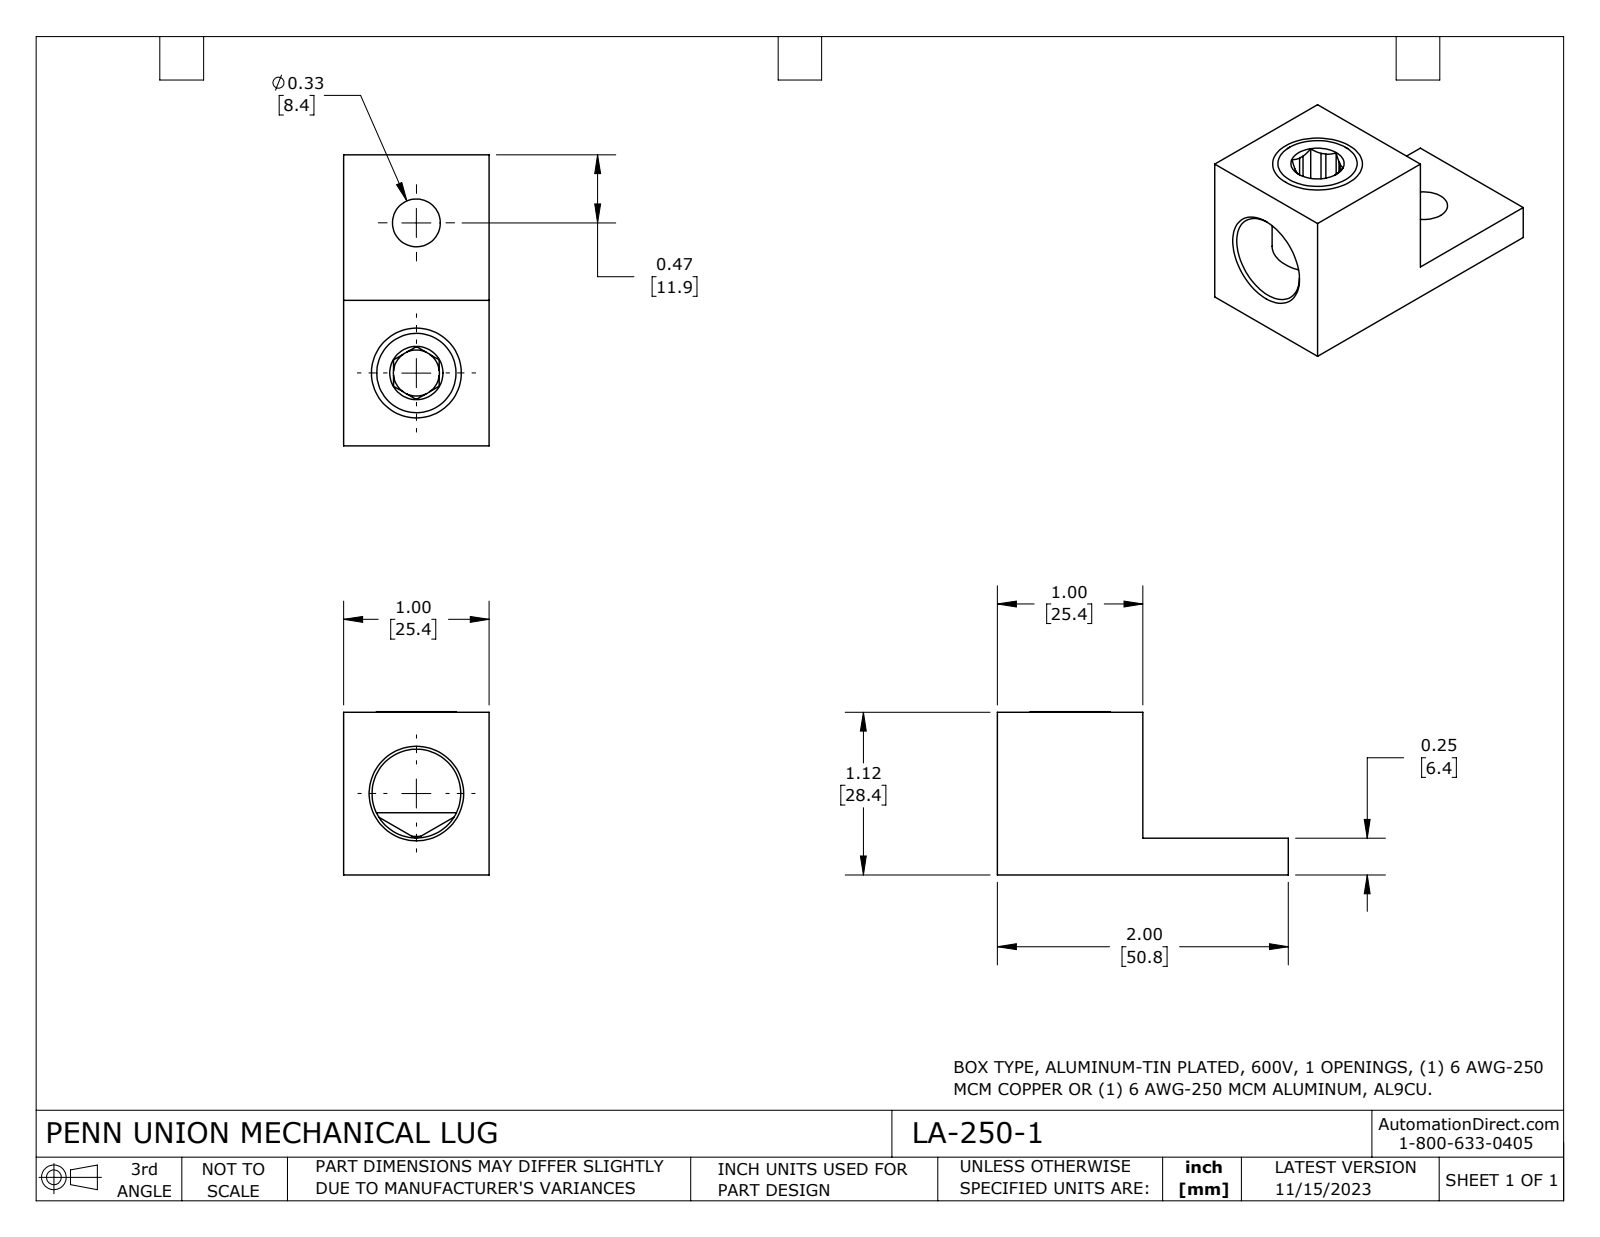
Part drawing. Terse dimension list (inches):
name: LA-250-1
written by: SolidWorks 2023 (CONFIG_CONTROL_DESIGN)
unit: in
bodies: 2 solids, 50 faces (27 planar, 10 cylindrical, 13 other)
size: 2 × 1.122 × 1
volume: 1.157 in³; area: 13.01 in²
holes: 1× ⌀0.316, 1× ⌀0.329, 1× ⌀0.578, 1× ⌀0.61
bosses: 1× ⌀0.625
face distances: 1, 0.252, 1.118, 0.866, 2, 0.314, 0.343, 0.657, 1.122, 0.87
hole spacings: 1.031
